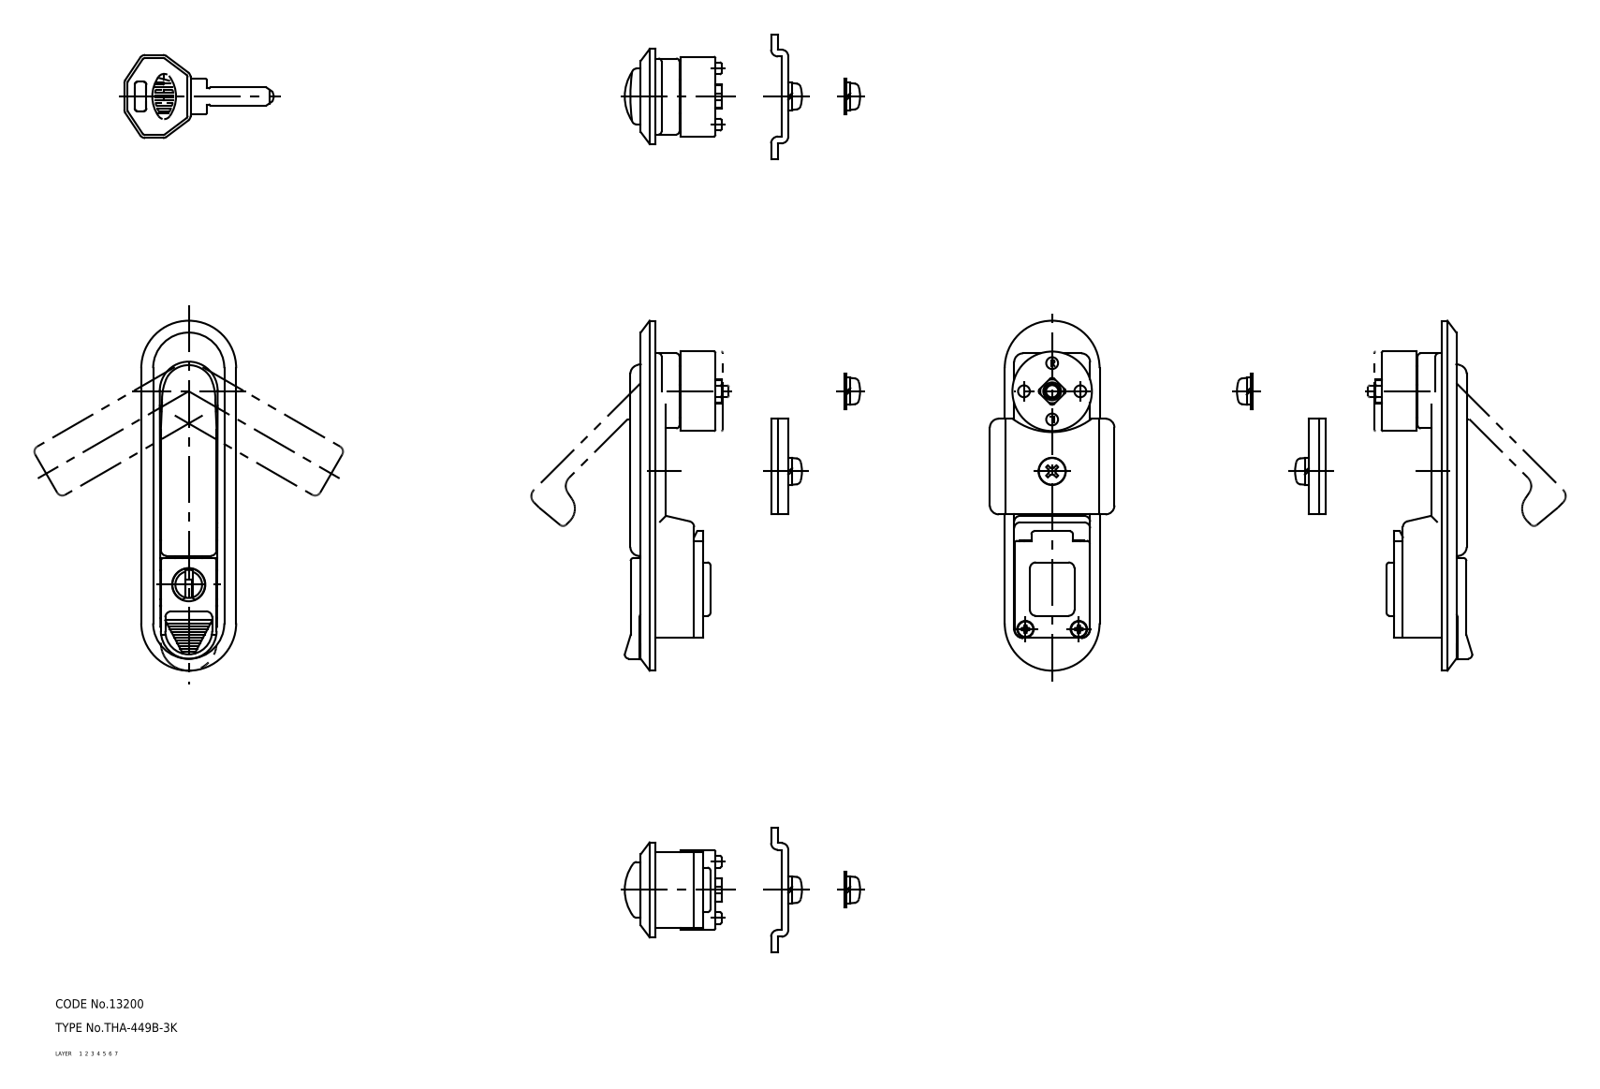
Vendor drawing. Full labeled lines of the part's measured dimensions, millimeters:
Part name (STEP PRODUCT): lock; shaft; screw_B; screw_A (+7 more)
STEP written by: CADfix (AUTOMOTIVE_DESIGN)
Units: millimetres
Bodies: 10 solids, 566 faces (0 planar, 0 cylindrical, 566 other)
Overall size (bounding box): 118 × 108.77 × 42
Volume: 43 588 mm³ · Surface area: 32 289 mm²
